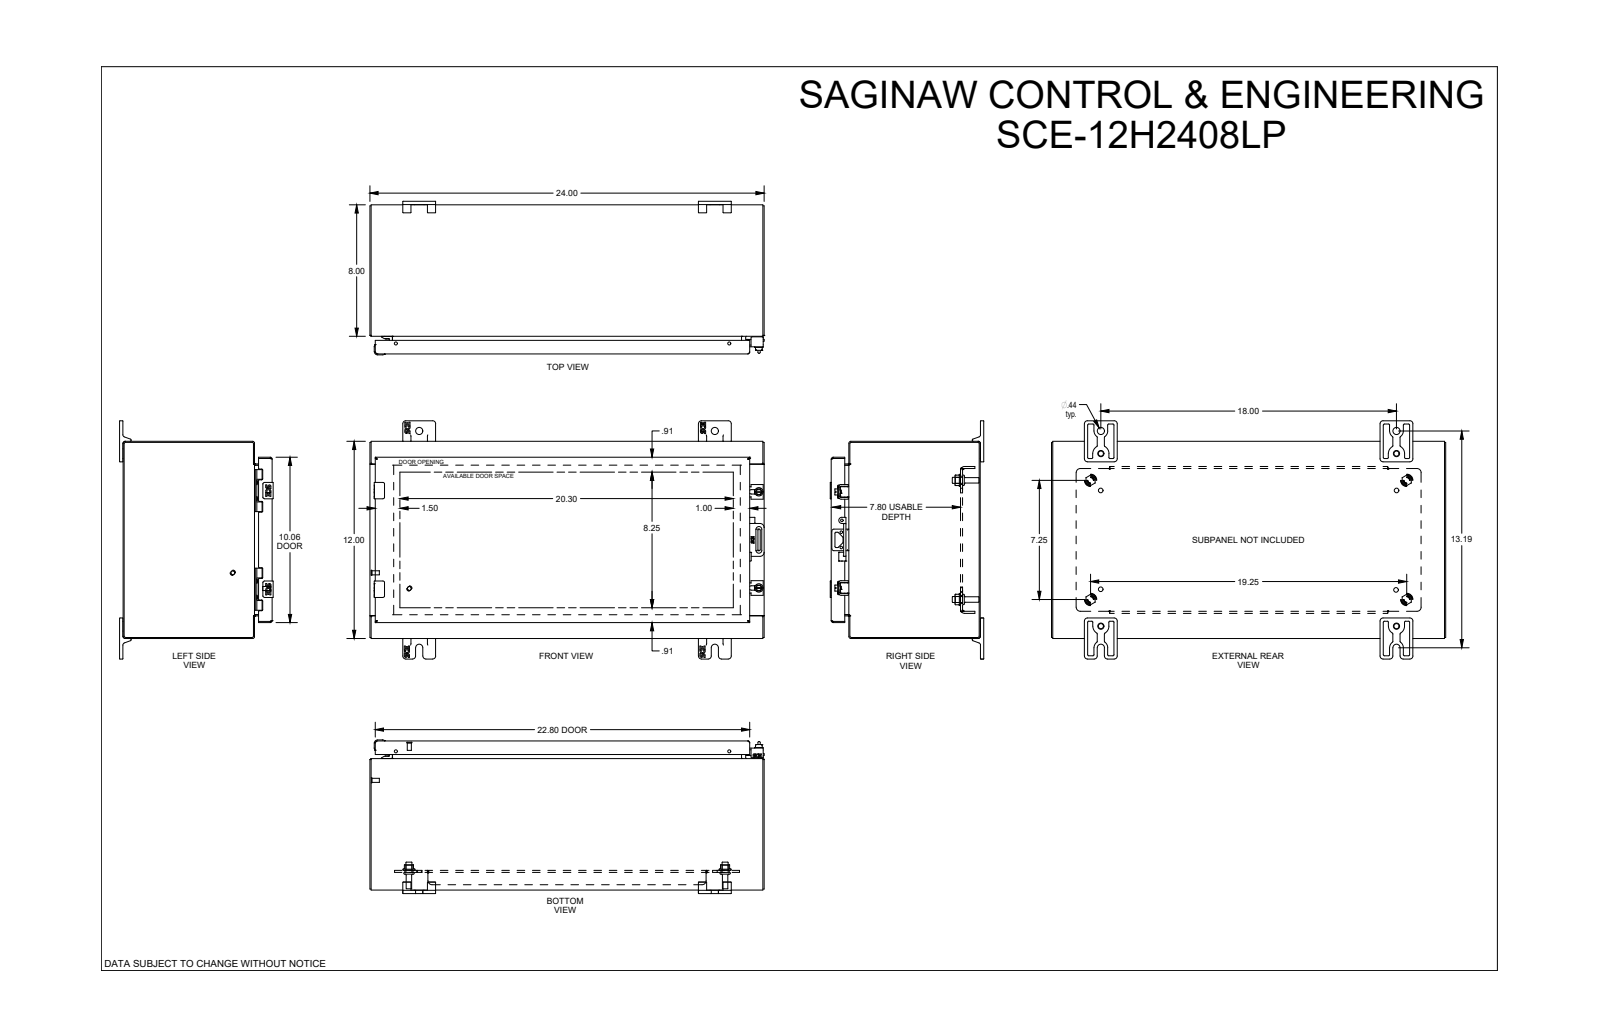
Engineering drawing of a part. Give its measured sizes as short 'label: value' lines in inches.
name: SCE-12H2408LP
written by: SolidWorks 2019 (AUTOMOTIVE_DESIGN)
unit: in
bodies: 56 solids, 3018 faces (1149 planar, 818 cylindrical, 1051 other)
size: 24 × 14.5 × 9.348
volume: 135.5 in³; area: 3 223 in²
holes: 4× ⌀0.172, 4× ⌀0.205, 4× ⌀0.218, 4× ⌀0.244, 4× ⌀0.266, 4× ⌀0.281, 4× ⌀0.31, 4× ⌀0.312, 4× ⌀0.367, 4× ⌀0.375, 4× ⌀0.437, 4× ⌀0.5
bosses: 7× ⌀0.17, 6× ⌀0.25, 5× ⌀0.248, 4× ⌀0.59, 4× ⌀0.376, 4× ⌀0.366, 4× ⌀0.332, 4× ⌀0.24
rounds: 114× R0.01, 88× R0.025, 48× R0.015, 32× R0.03, 30× R0.06, 21× R0.185, 18× R0.029, 12× R0.1
face distances: 0.075, 11.925, 0.06, 8.938, 9.013, 9.073, 8.998, 23.925, 12, 11.85
hole spacings: 0.02, 0.493, 0.875, 0.985, 1.741, 6, 8.897, 18.696
